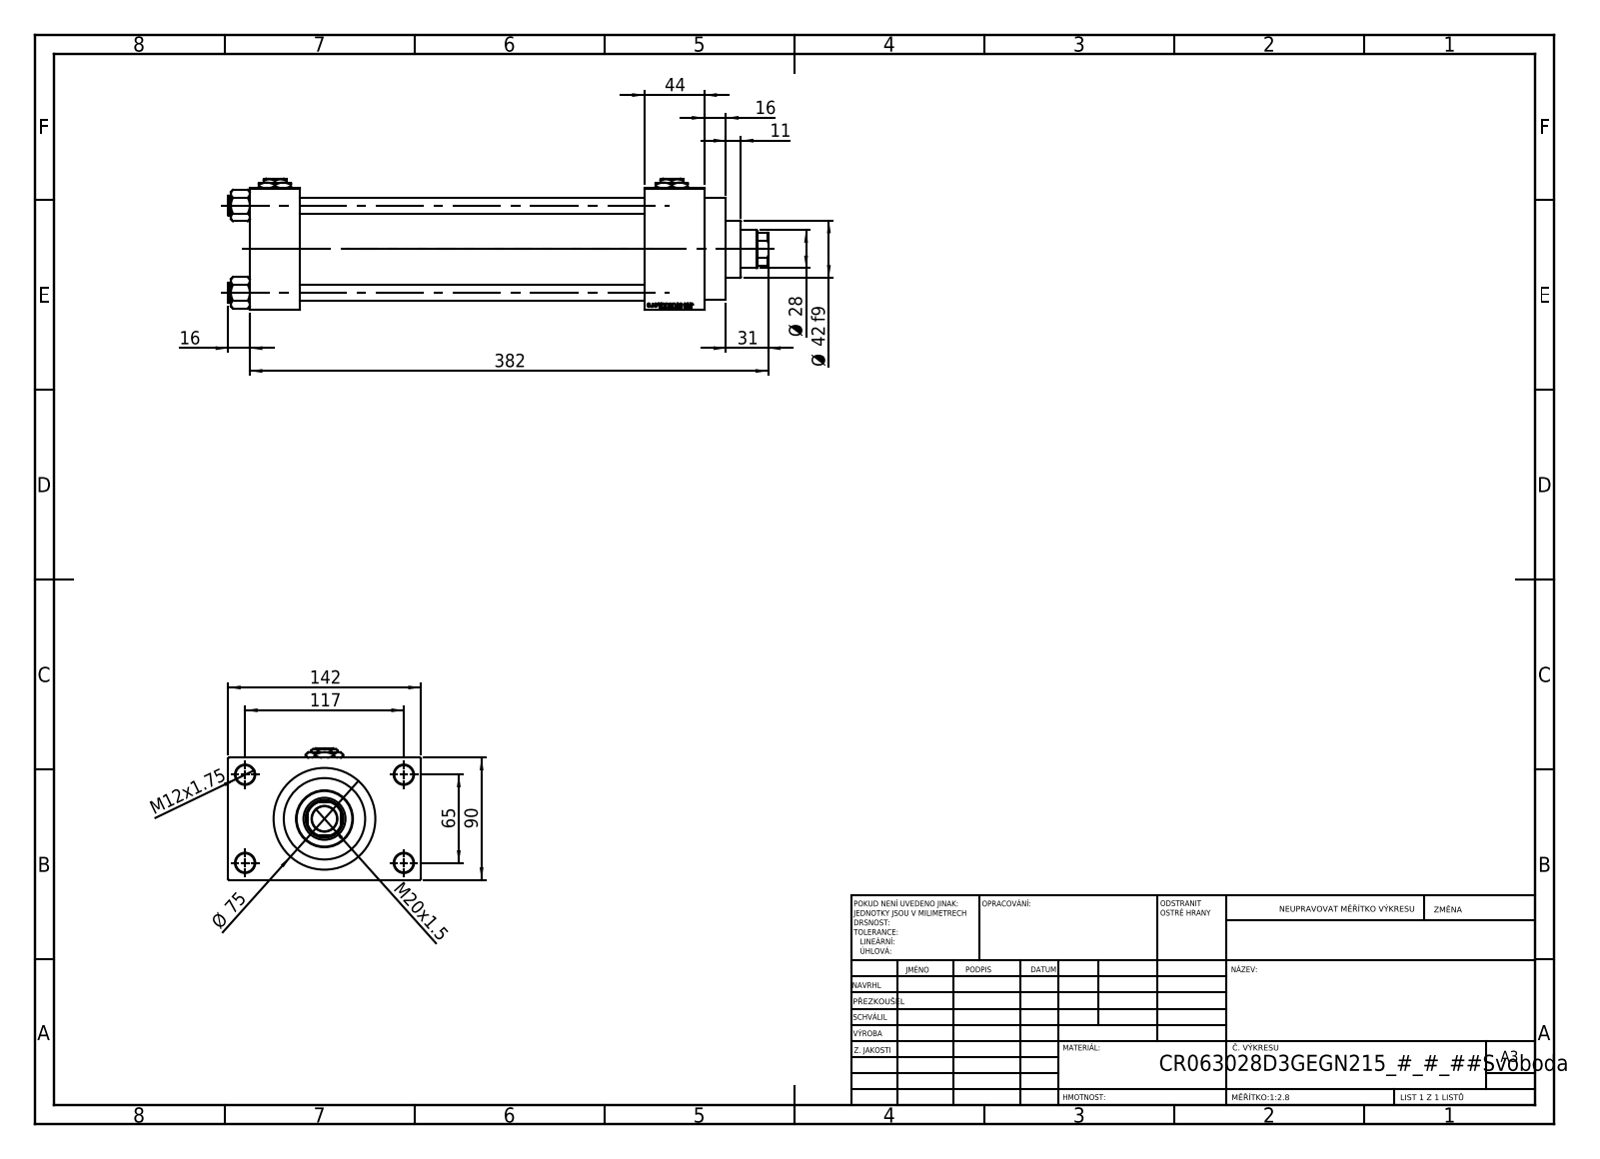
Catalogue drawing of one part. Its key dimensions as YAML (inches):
part_name: "Zatka_pro_OIL_PORT; V215CR_VCP_D; V215CR_D_TYCINKA; V215_VC_A (+2 more)"
step_written_by: "SolidWorks 2019 (CONFIG_CONTROL_DESIGN)"
units: inches
bodies: {solids: 13, faces: 1205, planar: 545, cylindrical: 100, other: 560}
overall_size: [15.669, 5.591, 3.819]
volume: 87.2
surface_area: 512.5
round_holes:
  - {diameter: 0.472, count: 4}
  - {diameter: 0.551, count: 4}
  - {diameter: 0.276, count: 2}
  - {diameter: 0.825, count: 2}
  - {diameter: 1.181, count: 2}
  - {diameter: 0.728, count: 1}
  - {diameter: 1.102, count: 1}
  - {diameter: 1.22, count: 1}
  - {diameter: 1.969, count: 1}
  - {diameter: 2.362, count: 1}
  - {diameter: 2.48, count: 1}
round_bosses_or_shafts:
  - {diameter: 0.591, count: 4}
  - {diameter: 2.953, count: 1}
  - {diameter: 2.717, count: 1}
  - {diameter: 1.654, count: 1}
partial_cylinders:
  - {radius: 0.531, count: 1}
face_to_face_distances: [3.543, 10, 1.457, 11.457, 11.732, 13.189, 1.732, 1.024, 4.567, 5.591]
hole_center_spacings: [1.037, 1.79, 2.531, 2.635, 2.748, 3.569, 4.383, 2.559]
